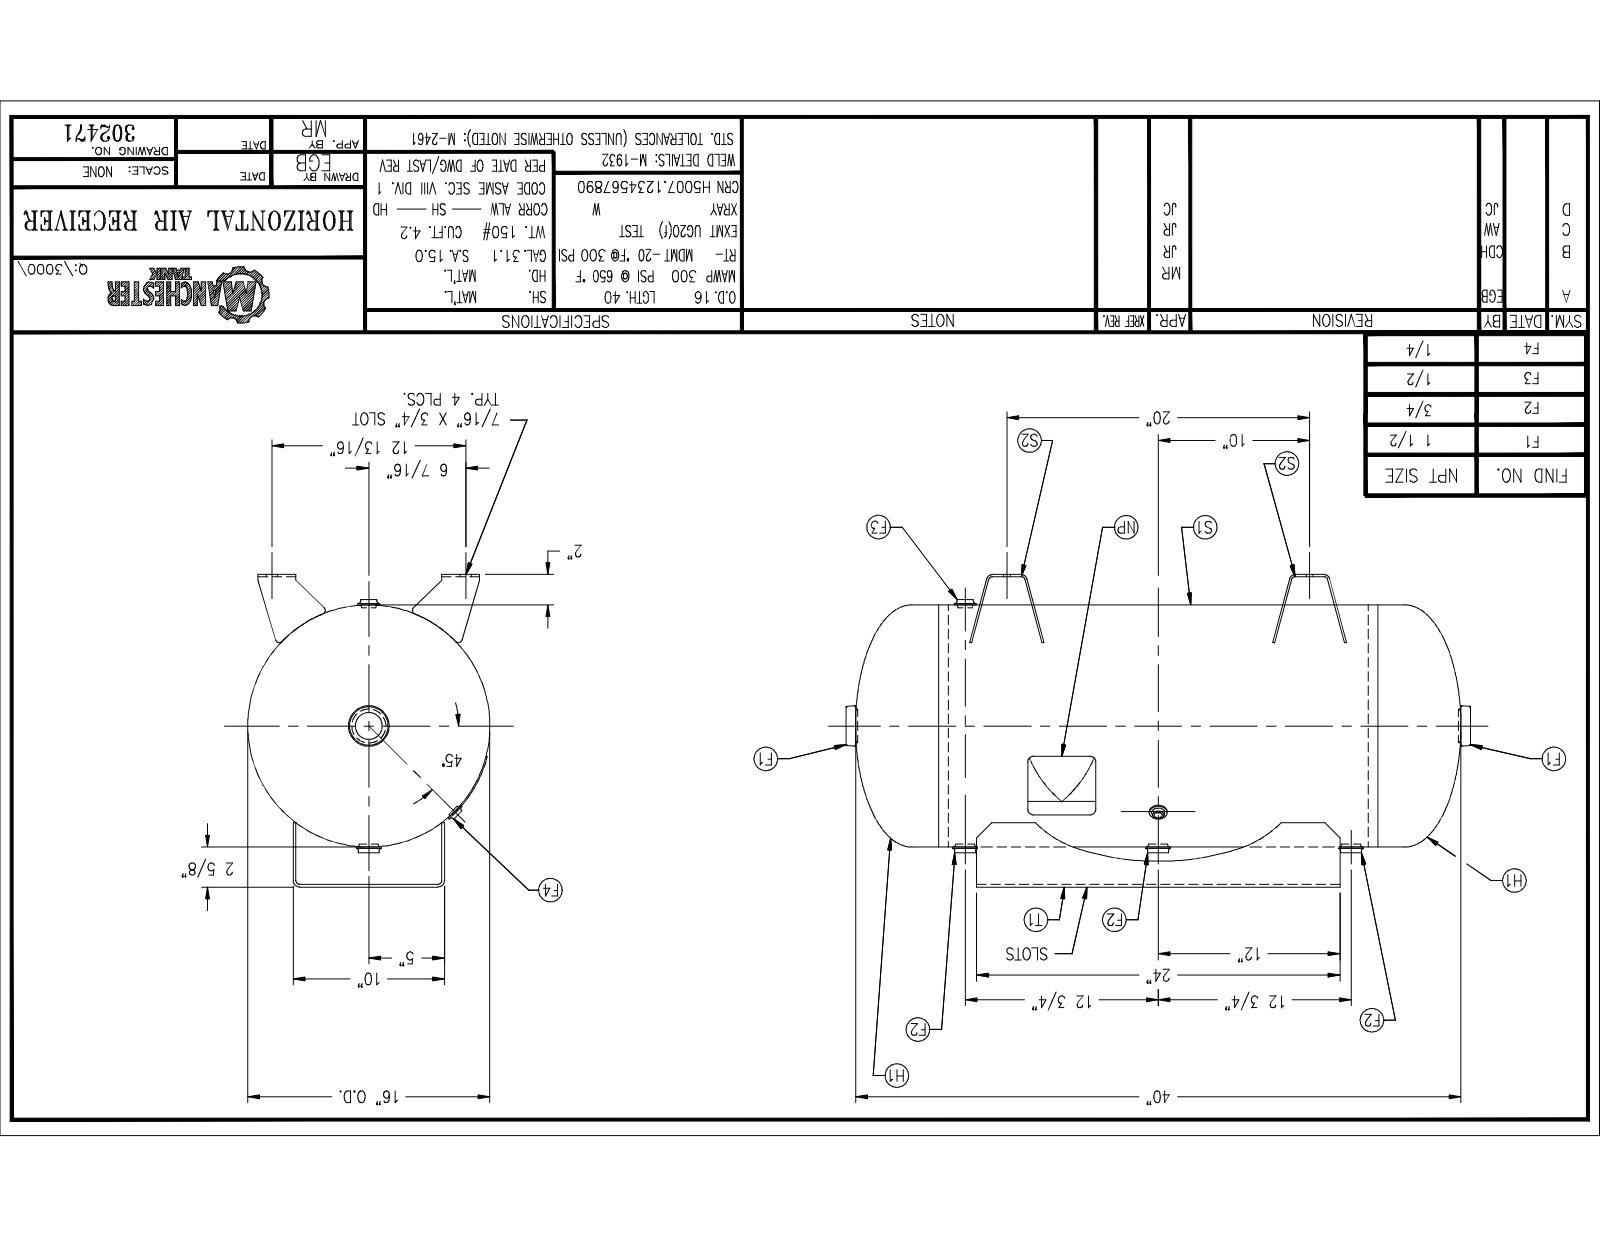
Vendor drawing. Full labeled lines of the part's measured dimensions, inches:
Part name (STEP PRODUCT): 302471
STEP written by: SolidWorks 2011 (CONFIG_CONTROL_DESIGN)
Units: inches
Bodies: 0 solids, 361 faces (141 planar, 141 cylindrical, 79 other)
Overall size (bounding box): 41.374 × 20.646 × 16
Round holes (diameter × count): ⌀1.05 ×3, ⌀0.54 ×1, ⌀0.84 ×1, ⌀1 ×1, ⌀1.9 ×1, ⌀3 ×1, ⌀15.626 ×1, ⌀15.638 ×1
Round bosses / shafts (diameter × count): ⌀2.063 ×3, ⌀16 ×1, ⌀3.031 ×1, ⌀2.375 ×1, ⌀1.813 ×1, ⌀1.5 ×1
Partial cylindrical surfaces — rounded edges, fillets, slot ends (radius × count): R0.203 ×20, R0.187 ×8, R0.188 ×8, R0.219 ×8, R8 ×8, R0.25 ×6, R0.384 ×4, R0.429 ×2
Main face-to-face distances: 0.179, 9.821, 19.32, 0.134, 10, 9.642, 19.454, 19.321, 0.133, 0.134
Hole centre spacings: 12.75, 25.5
